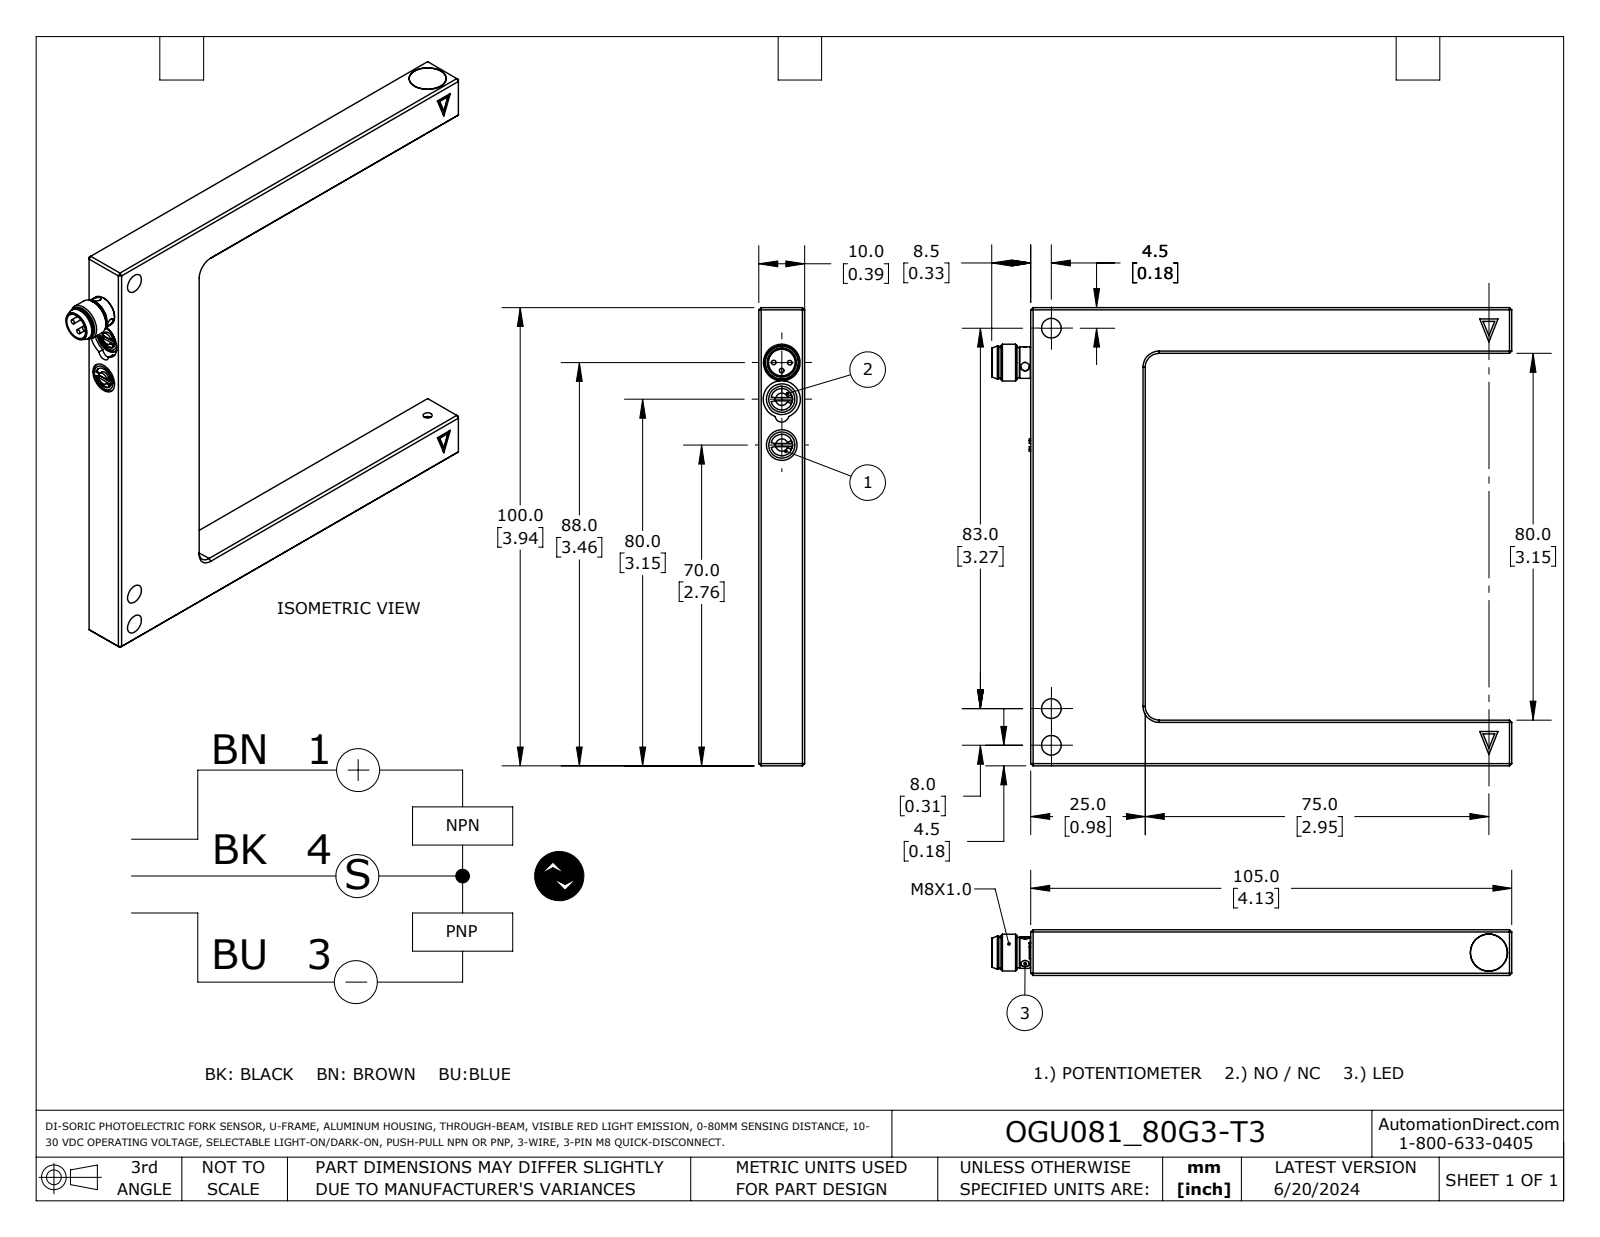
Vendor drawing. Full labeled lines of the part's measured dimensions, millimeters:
Part name (STEP PRODUCT): OGU08180G3-T3
STEP written by: SolidWorks 2023 (AUTOMOTIVE_DESIGN)
Units: millimetres
Bodies: 1 solid, 163 faces (103 planar, 49 cylindrical, 11 other)
Overall size (bounding box): 113.5 × 100 × 10
Volume: 40 570 mm³ · Surface area: 14 630 mm²
Round holes (diameter × count): ⌀1.9 ×3, ⌀4.3 ×3, ⌀6.7 ×3, ⌀4.7 ×2, ⌀8.1 ×2, ⌀2 ×1, ⌀5.8 ×1
Round bosses / shafts (diameter × count): ⌀1 ×3, ⌀8.1 ×1, ⌀8 ×1, ⌀7.2 ×1, ⌀6.9 ×1, ⌀6.6 ×1, ⌀6.4 ×1, ⌀5 ×1
Partial cylindrical surfaces — rounded edges, fillets, slot ends (radius × count): R1.5 ×3, R1.3 ×2, R2 ×2, R2.3 ×2, R3 ×2
Main face-to-face distances: 10, 90, 100, 80, 25, 63.6, 13.4, 105, 77.1, 50.2
Hole centre spacings: 8, 10, 18, 83, 91
